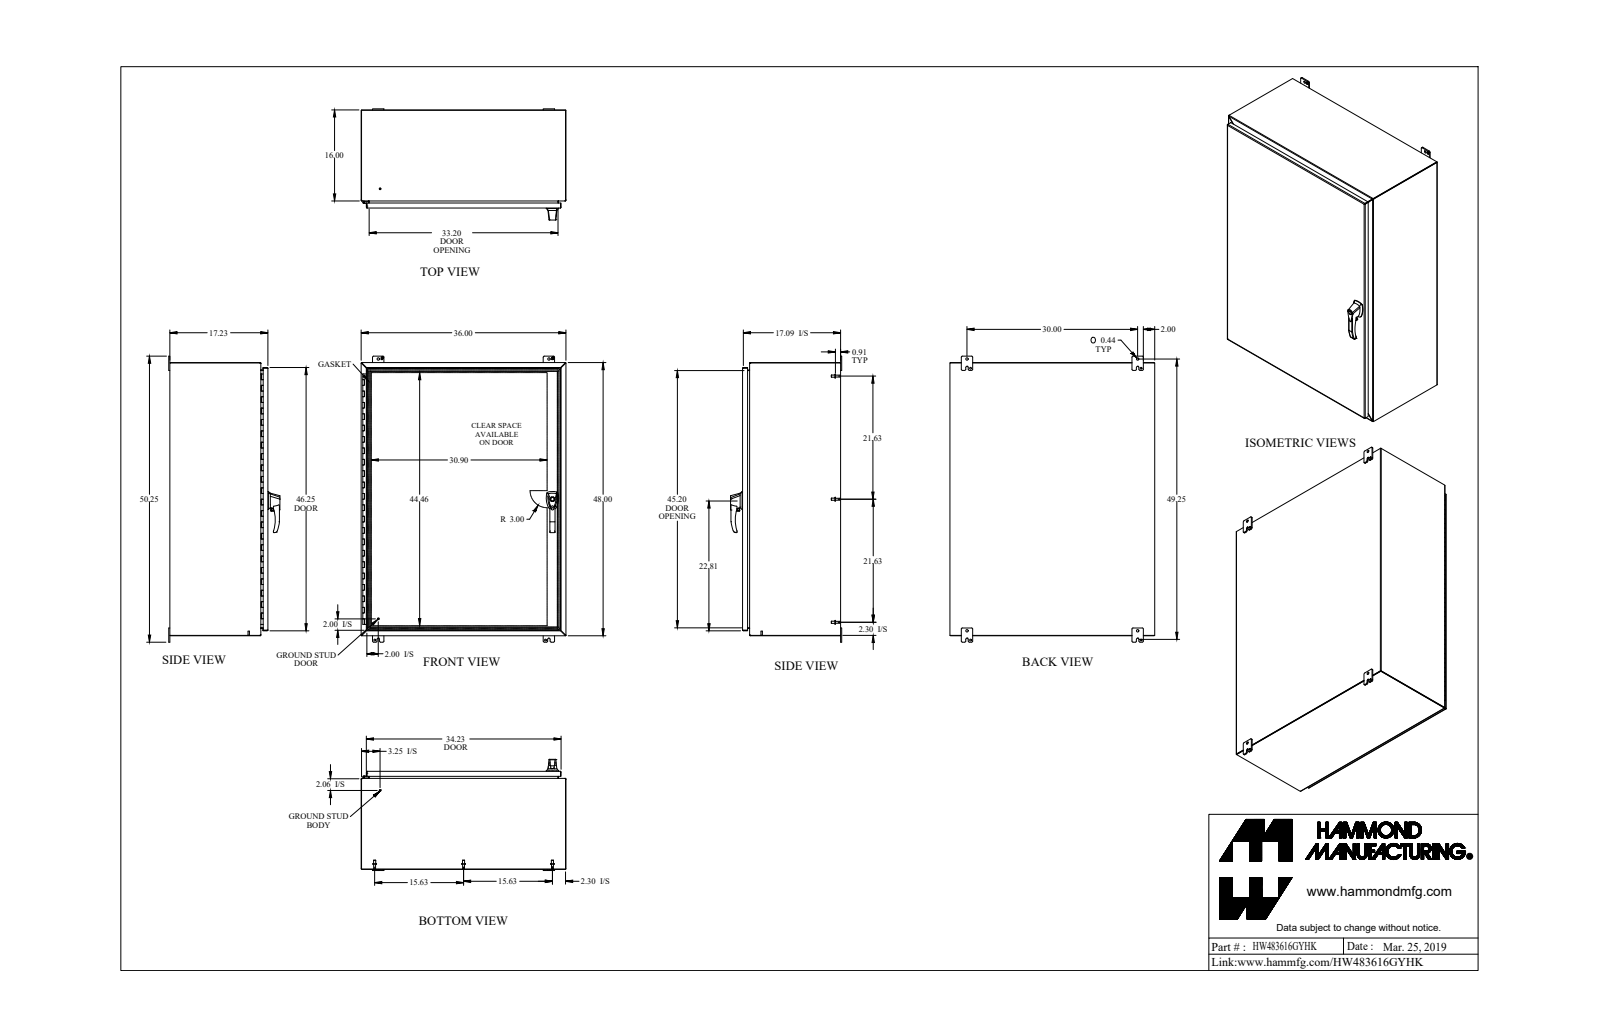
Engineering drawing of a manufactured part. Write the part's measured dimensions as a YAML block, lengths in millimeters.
part_name: "HW483616GYHK"
step_written_by: "SolidWorks 2018 (AUTOMOTIVE_DESIGN)"
units: millimeters
bodies: {solids: 49, faces: 1635, planar: 754, cylindrical: 686, other: 195}
overall_size: [1276.4, 914.4, 496.2]
volume: 9380000
surface_area: 9299000
round_holes:
  - {diameter: 4.5, count: 6}
  - {diameter: 6.4, count: 4}
  - {diameter: 8, count: 4}
  - {diameter: 5, count: 3}
  - {diameter: 6.7, count: 3}
  - {diameter: 10.5, count: 3}
  - {diameter: 6.5, count: 2}
  - {diameter: 10, count: 2}
  - {diameter: 11.1, count: 2}
  - {diameter: 4.7, count: 1}
  - {diameter: 5.9, count: 1}
  - {diameter: 8.5, count: 1}
round_bosses_or_shafts:
  - {diameter: 9.5, count: 13}
  - {diameter: 16.5, count: 8}
  - {diameter: 8.4, count: 8}
  - {diameter: 6.4, count: 6}
  - {diameter: 4, count: 6}
  - {diameter: 25.4, count: 3}
  - {diameter: 16, count: 2}
  - {diameter: 13, count: 2}
partial_cylinders:
  - {radius: 4.8, count: 24}
  - {radius: 0.9, count: 14}
  - {radius: 2.7, count: 14}
  - {radius: 2.9, count: 12}
  - {radius: 4.7, count: 12}
  - {radius: 6.4, count: 11}
  - {radius: 3.2, count: 9}
  - {radius: 1, count: 8}
face_to_face_distances: [1.8, 435.3, 433.5, 2.4, 437.7, 435.9, 912.6, 1217.4, 910.7, 914.4]
hole_center_spacings: [511, 511, 1022, 28.2, 511, 762, 778.8, 994.3]
